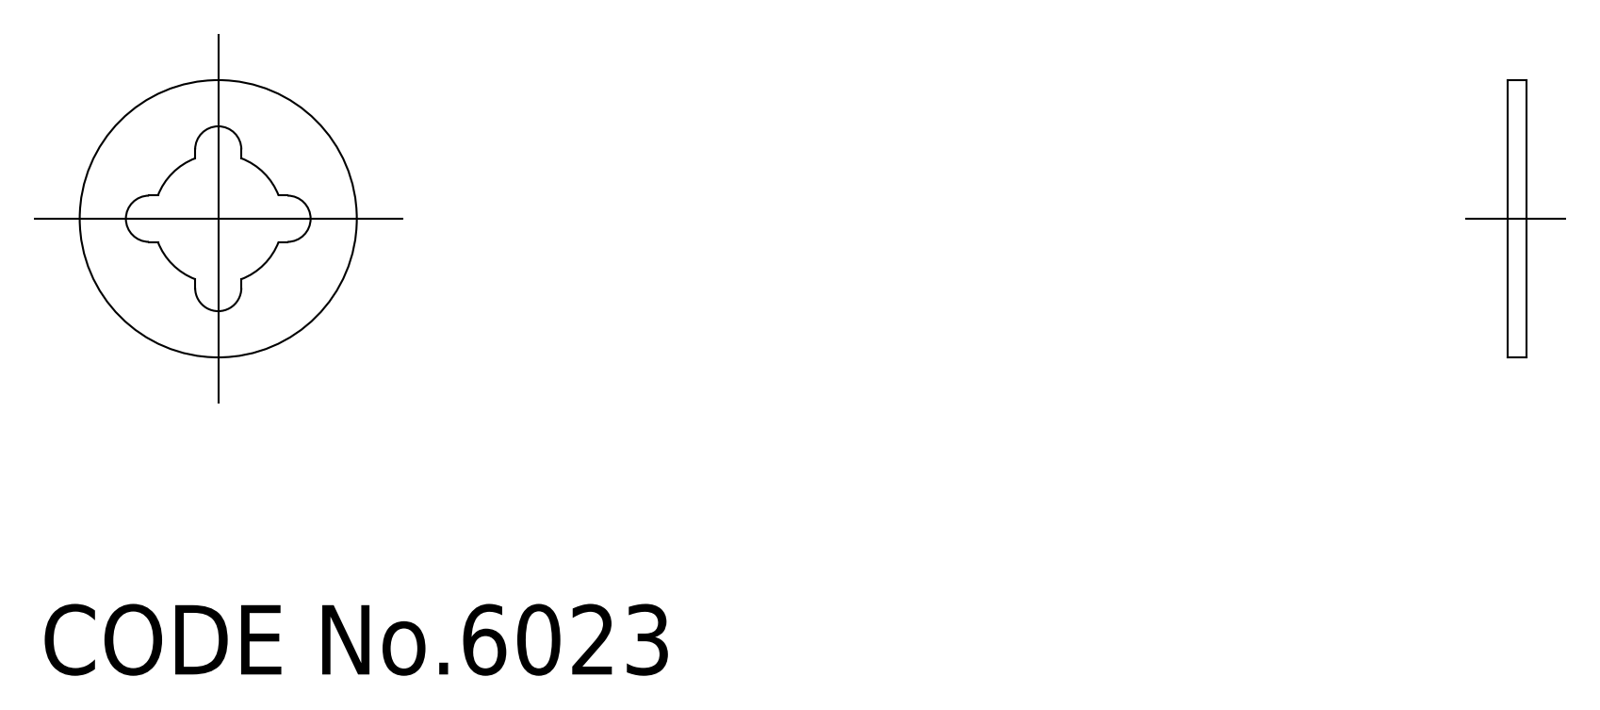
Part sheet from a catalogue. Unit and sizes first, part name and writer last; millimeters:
Units: millimetres
Overall size (bounding box): 12 × 12 × 0.8
Volume: 64 mm³ · Surface area: 210 mm²
Bodies: 1 solid, 20 faces (0 planar, 0 cylindrical, 20 other)
Part name (STEP PRODUCT): washer
STEP written by: CADfix (AUTOMOTIVE_DESIGN)
